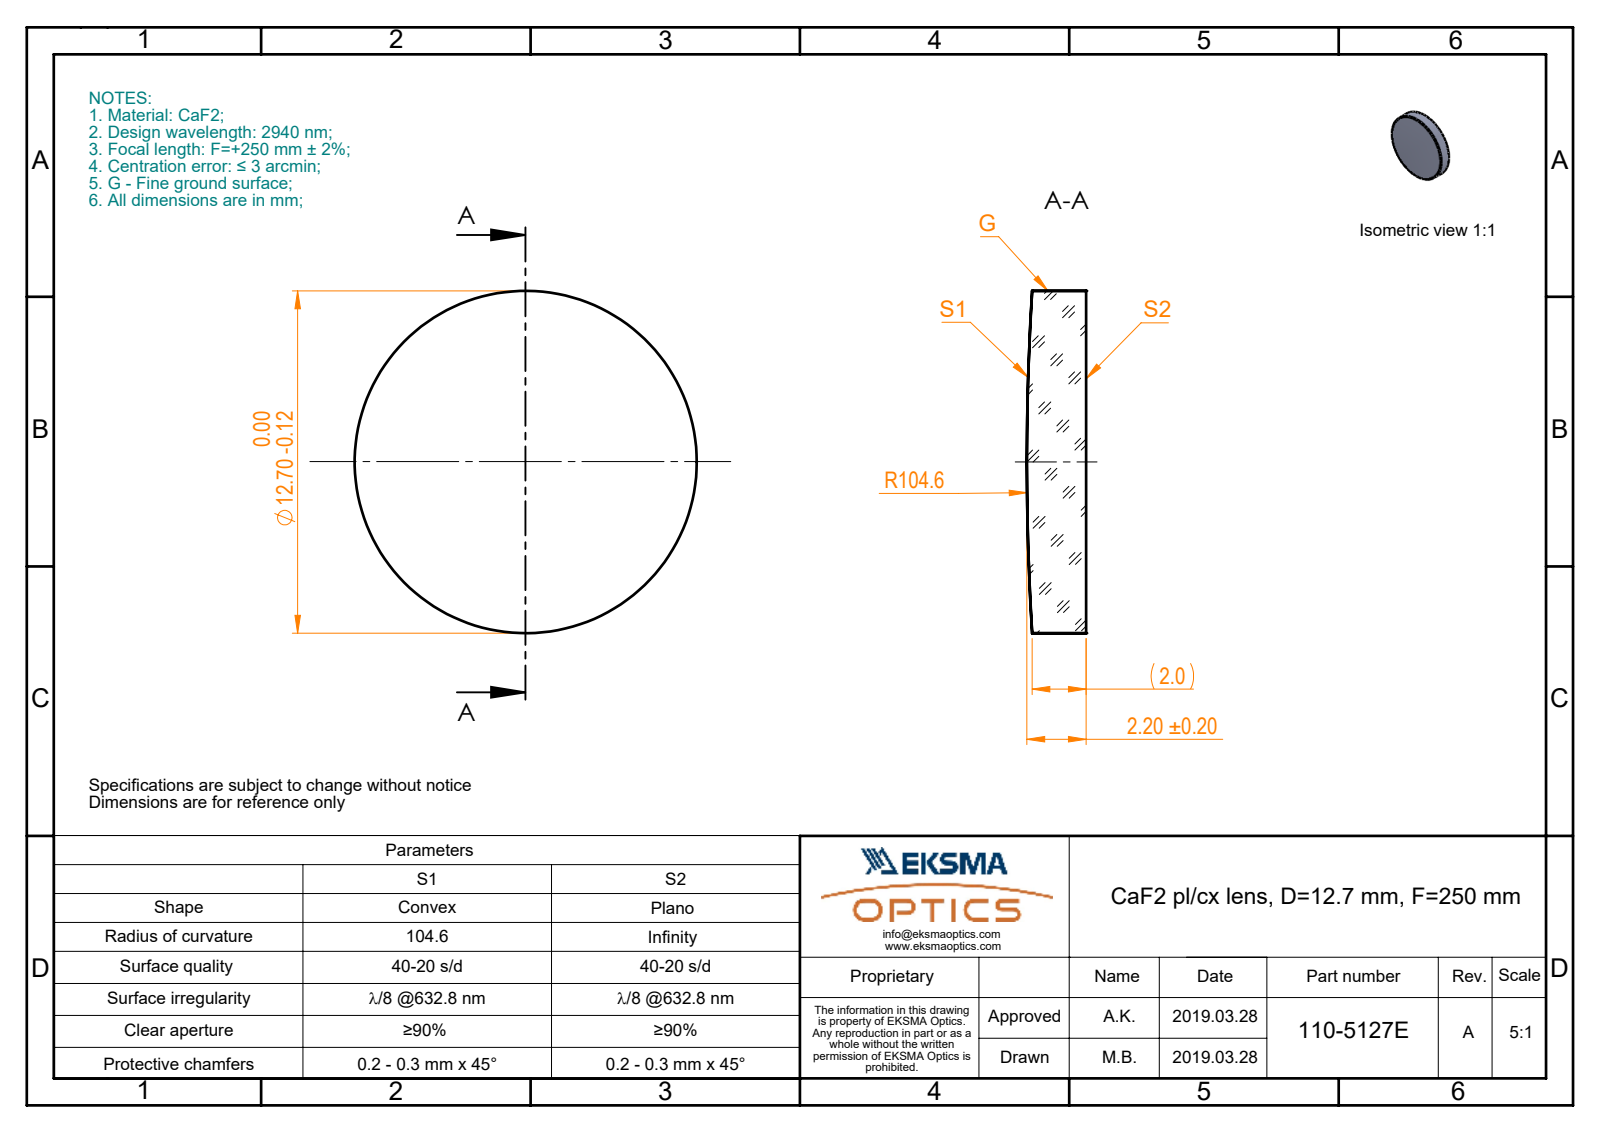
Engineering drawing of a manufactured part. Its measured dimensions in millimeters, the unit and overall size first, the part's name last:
Units: millimetres
Overall size (bounding box): 12.7 × 12.7 × 2.2
Round bosses / shafts (diameter × count): ⌀12.7 ×1
Volume: 266 mm³ · Surface area: 334 mm²
Bodies: 1 solid, 5 faces (1 planar, 2 cylindrical, 2 other)
Part name (STEP PRODUCT): 110-5127E CaF2 pl-cx 12.7 F250
STEP written by: SolidWorks 2017 (CONFIG_CONTROL_DESIGN)
